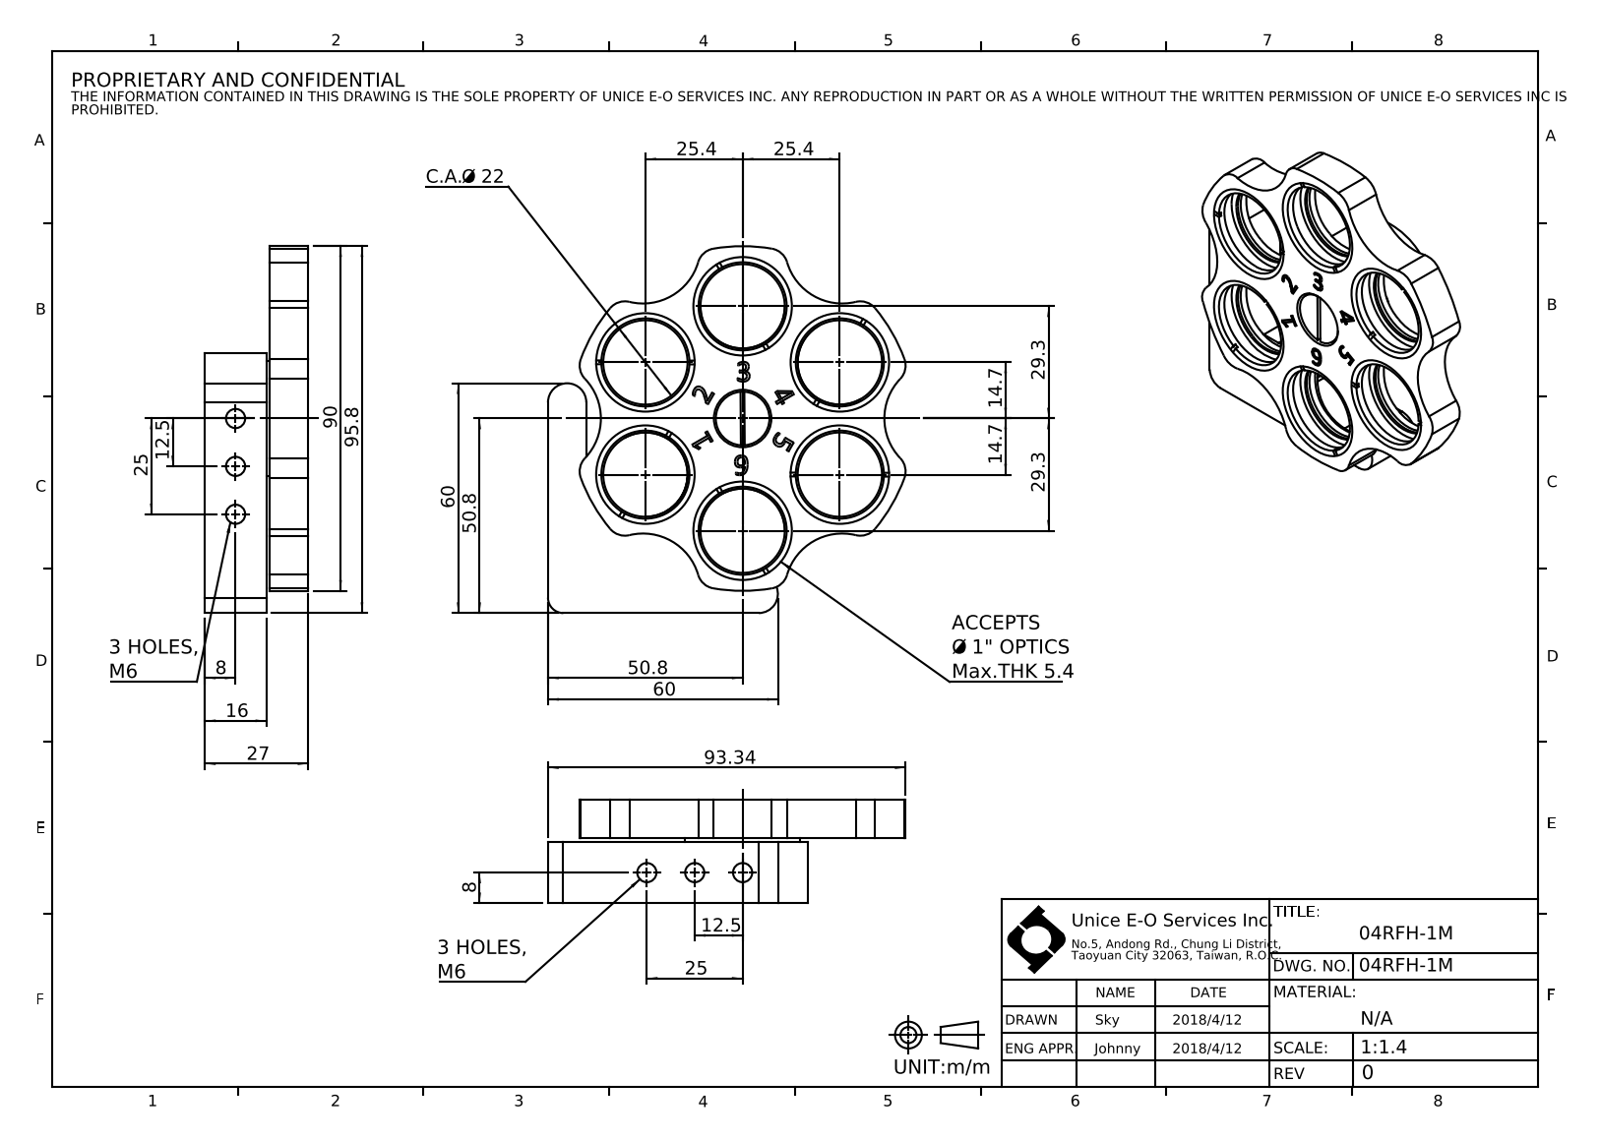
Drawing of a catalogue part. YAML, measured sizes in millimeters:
part_name: "04RFH-1M"
step_written_by: "SolidWorks 2016 (CONFIG_CONTROL_DESIGN)"
units: millimeters
bodies: {solids: 21, faces: 408, planar: 114, cylindrical: 191, other: 103}
overall_size: [95.8, 93.34, 27]
volume: 69788
surface_area: 37733
round_holes:
  - {diameter: 1.5, count: 12}
  - {diameter: 5, count: 10}
  - {diameter: 22, count: 8}
  - {diameter: 19.5, count: 6}
  - {diameter: 26.3, count: 6}
  - {diameter: 7, count: 1}
  - {diameter: 10, count: 1}
  - {diameter: 15, count: 1}
round_bosses_or_shafts:
  - {diameter: 25, count: 6}
  - {diameter: 26.3, count: 4}
  - {diameter: 6, count: 3}
  - {diameter: 30, count: 1}
  - {diameter: 14, count: 1}
  - {diameter: 5, count: 1}
partial_cylinders:
  - {radius: 5, count: 14}
  - {radius: 15, count: 6}
  - {radius: 10, count: 2}
  - {radius: 20, count: 2}
  - {radius: 4, count: 1}
  - {radius: 11, count: 1}
  - {radius: 17, count: 1}
  - {radius: 45, count: 1}
face_to_face_distances: [1, 3, 4.6, 10, 16, 5.6, 17, 11, 27, 4]
hole_center_spacings: [29.3, 36.08, 11, 51.93, 25.63, 41.59, 50.75, 60.53]
